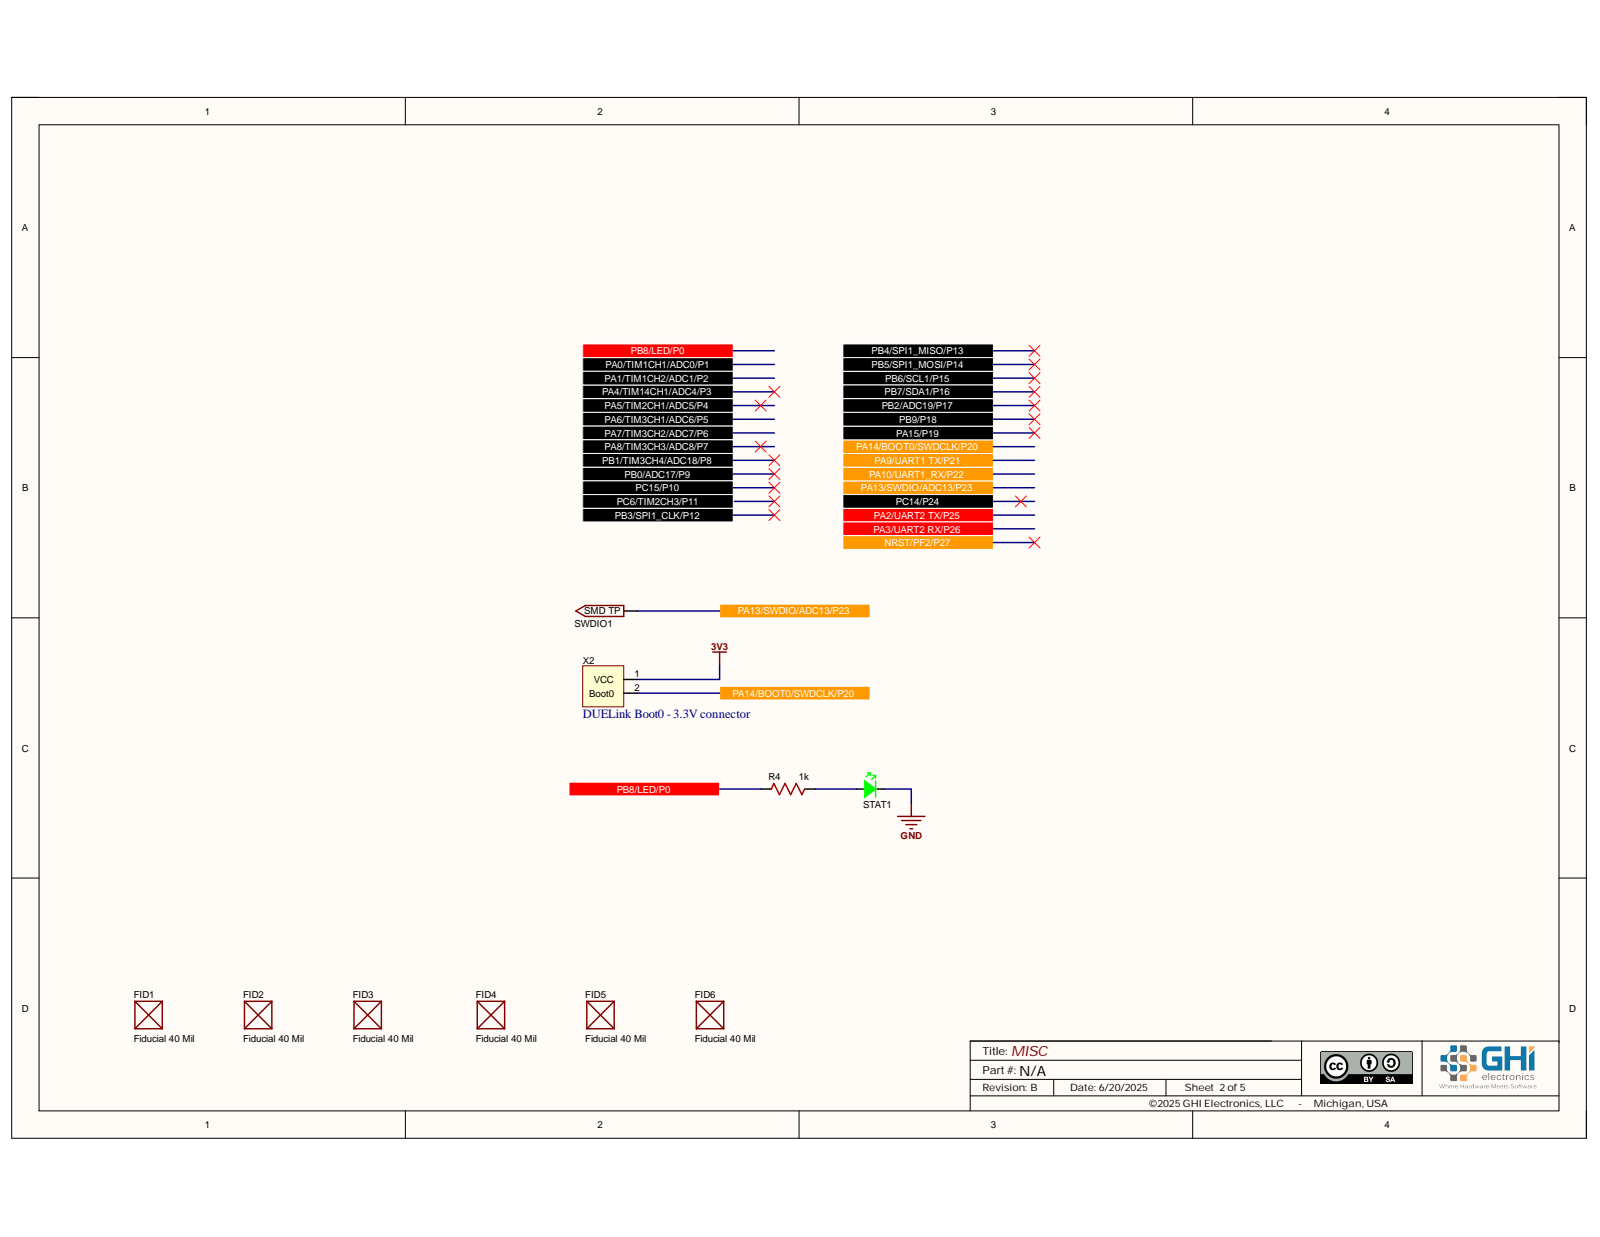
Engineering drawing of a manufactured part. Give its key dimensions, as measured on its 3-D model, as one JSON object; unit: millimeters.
{"part_name": "PCB; Board; R1; 6673943136 (+7 more)", "step_written_by": "Open CASCADE 7.5 (AUTOMOTIVE_DESIGN)", "units": "millimeters", "bodies": {"solids": 123, "faces": 2133, "planar": 1480, "cylindrical": 317, "other": 336}, "overall_size": [42, 38.9, 32.65], "volume_mm3": 12119, "surface_area_mm2": 8903, "round_holes": [[3, 4], [2.5, 3], [1.02, 2], [1.2, 2], [2.35, 2], [19.5, 1]], "round_bosses_or_shafts": [[1.6, 4], [1.2, 2], [22, 1], [15.85, 1]], "partial_cylinders_radius": [[0.12, 35], [0.15, 14], [0.15, 14], [0.2, 7], [0.13, 6], [0.33, 4], [2, 4], [3.5, 4]], "face_to_face_distances": [1.6, 22.2, 22, 2.7, 19.5, 13, 9.2, 32, 10.3, 10], "hole_center_spacings": [4.05, 5.66, 11.5, 14, 17.11, 20.86, 22.19, 25]}
